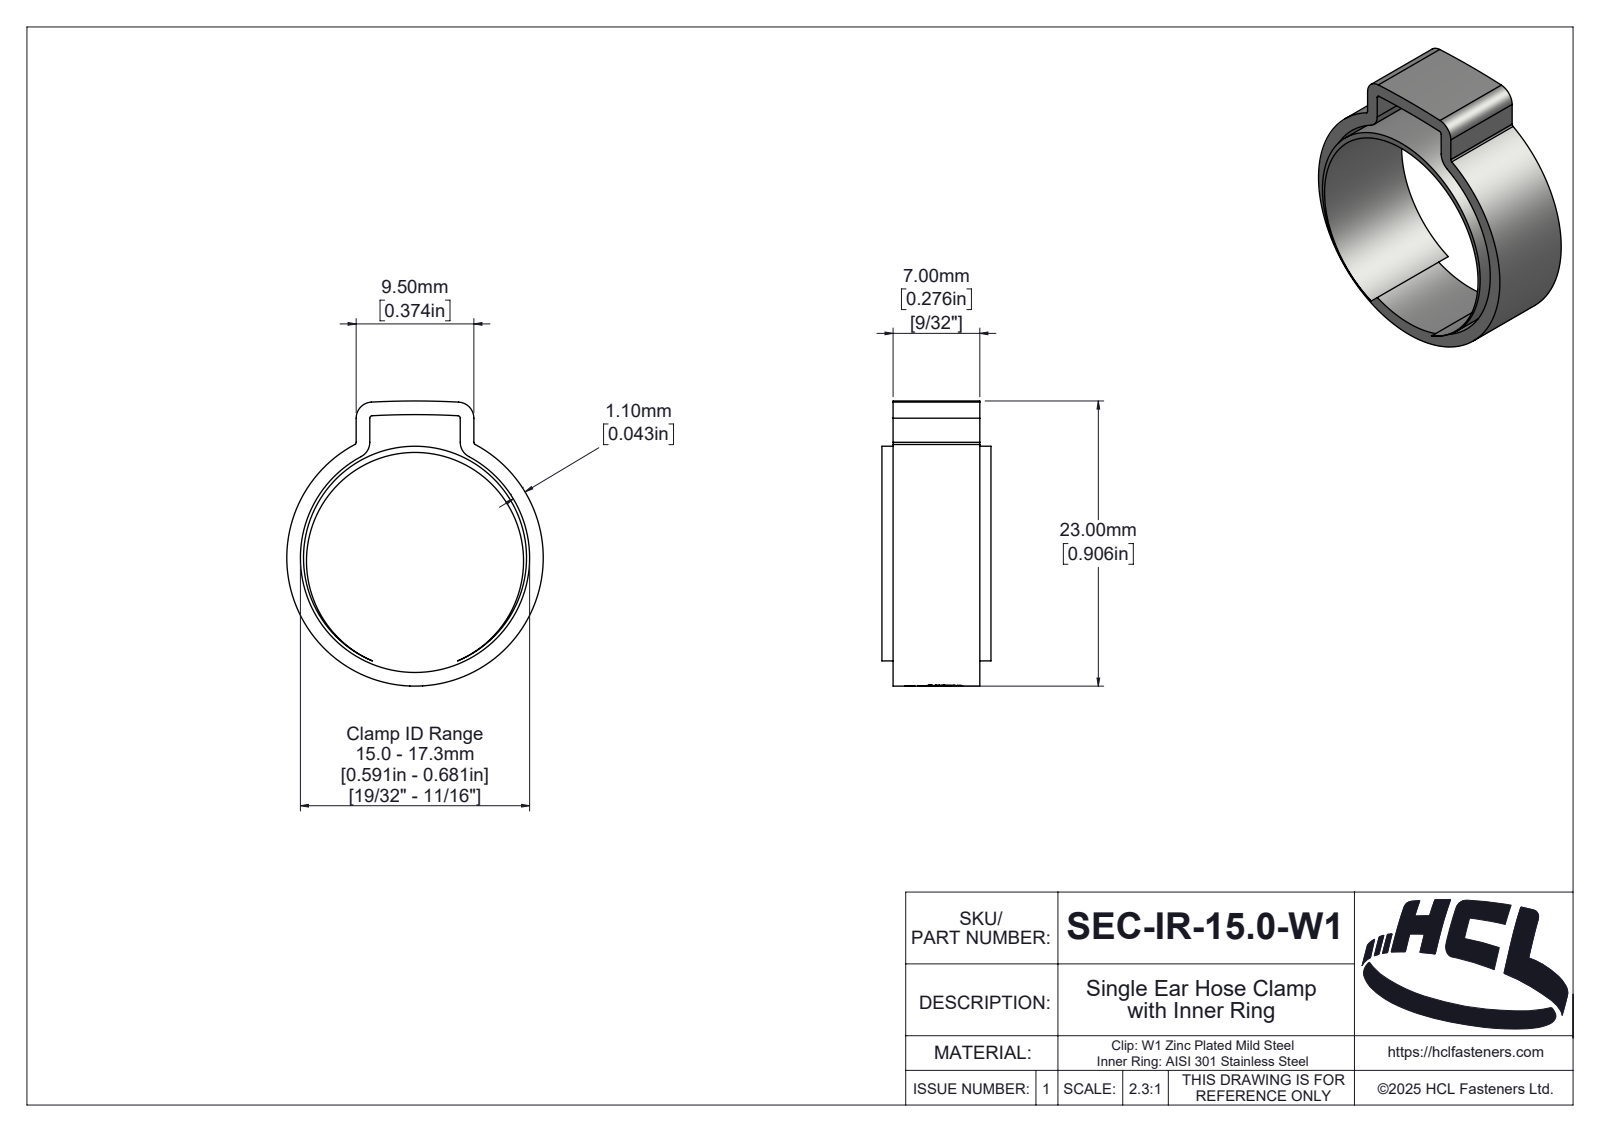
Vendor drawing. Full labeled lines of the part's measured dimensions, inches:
Part name (STEP PRODUCT): SEC-IR-15.0-W1
STEP written by: SolidWorks 2025 (AUTOMOTIVE_DESIGN)
Units: inches
Bodies: 2 solids, 131 faces (10 planar, 72 cylindrical, 49 other)
Overall size (bounding box): 0.906 × 0.815 × 0.346
Volume: 0.039 in³ · Surface area: 3.054 in²
Round holes (diameter × count): ⌀0.69 ×1, ⌀0.728 ×1
Round bosses / shafts (diameter × count): ⌀0.815 ×1, ⌀0.709 ×1
Partial cylindrical surfaces — rounded edges, fillets, slot ends (radius × count): R0.008 ×4, R0.051 ×4, R0.008 ×1, R0.032 ×1, R0.04 ×1, R0.042 ×1, R0.05 ×1, R0.071 ×1
Main face-to-face distances: 0.276, 0.043, 0.331, 0.035, 0.311, 0.374, 0.287, 0.346, 0.176, 0.133
